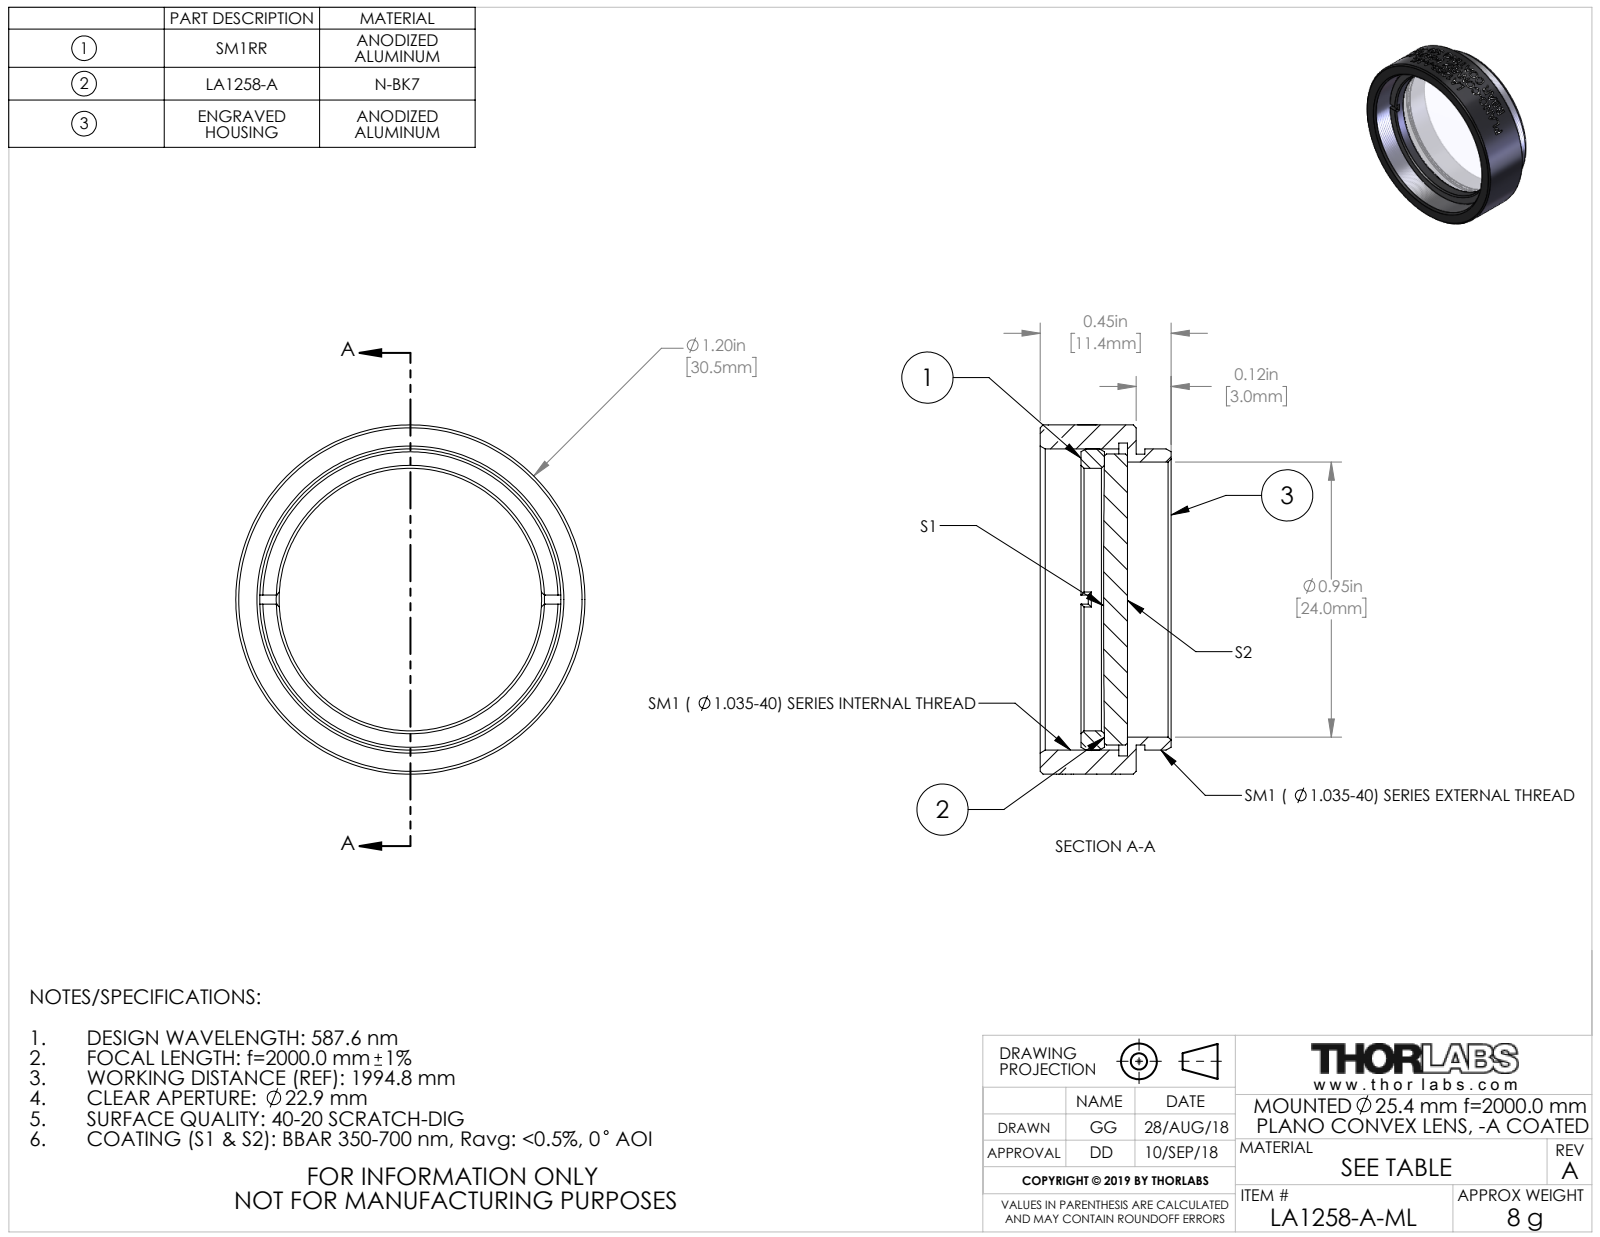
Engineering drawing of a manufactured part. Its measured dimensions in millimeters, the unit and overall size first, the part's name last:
Units: millimetres
Overall size (bounding box): 30.48 × 30.48 × 11.43
Round holes (diameter × count): ⌀22.91 ×1, ⌀24 ×1, ⌀26.29 ×1, ⌀27.3 ×1
Round bosses / shafts (diameter × count): ⌀30.48 ×1, ⌀26.29 ×1, ⌀25.4 ×1, ⌀25.37 ×1
Main face-to-face distances: 0.77, 8.39, 7.62, 2.78, 2.01, 5.61, 4.81, 4.04, 2.03, 3.58
Volume: 3 112 mm³ · Surface area: 4 296 mm²
Bodies: 3 solids, 179 faces (20 planar, 131 cylindrical, 28 other)
Part name (STEP PRODUCT): TTN162140-E0W
STEP written by: SolidWorks 2018 (CONFIG_CONTROL_DESIGN)
